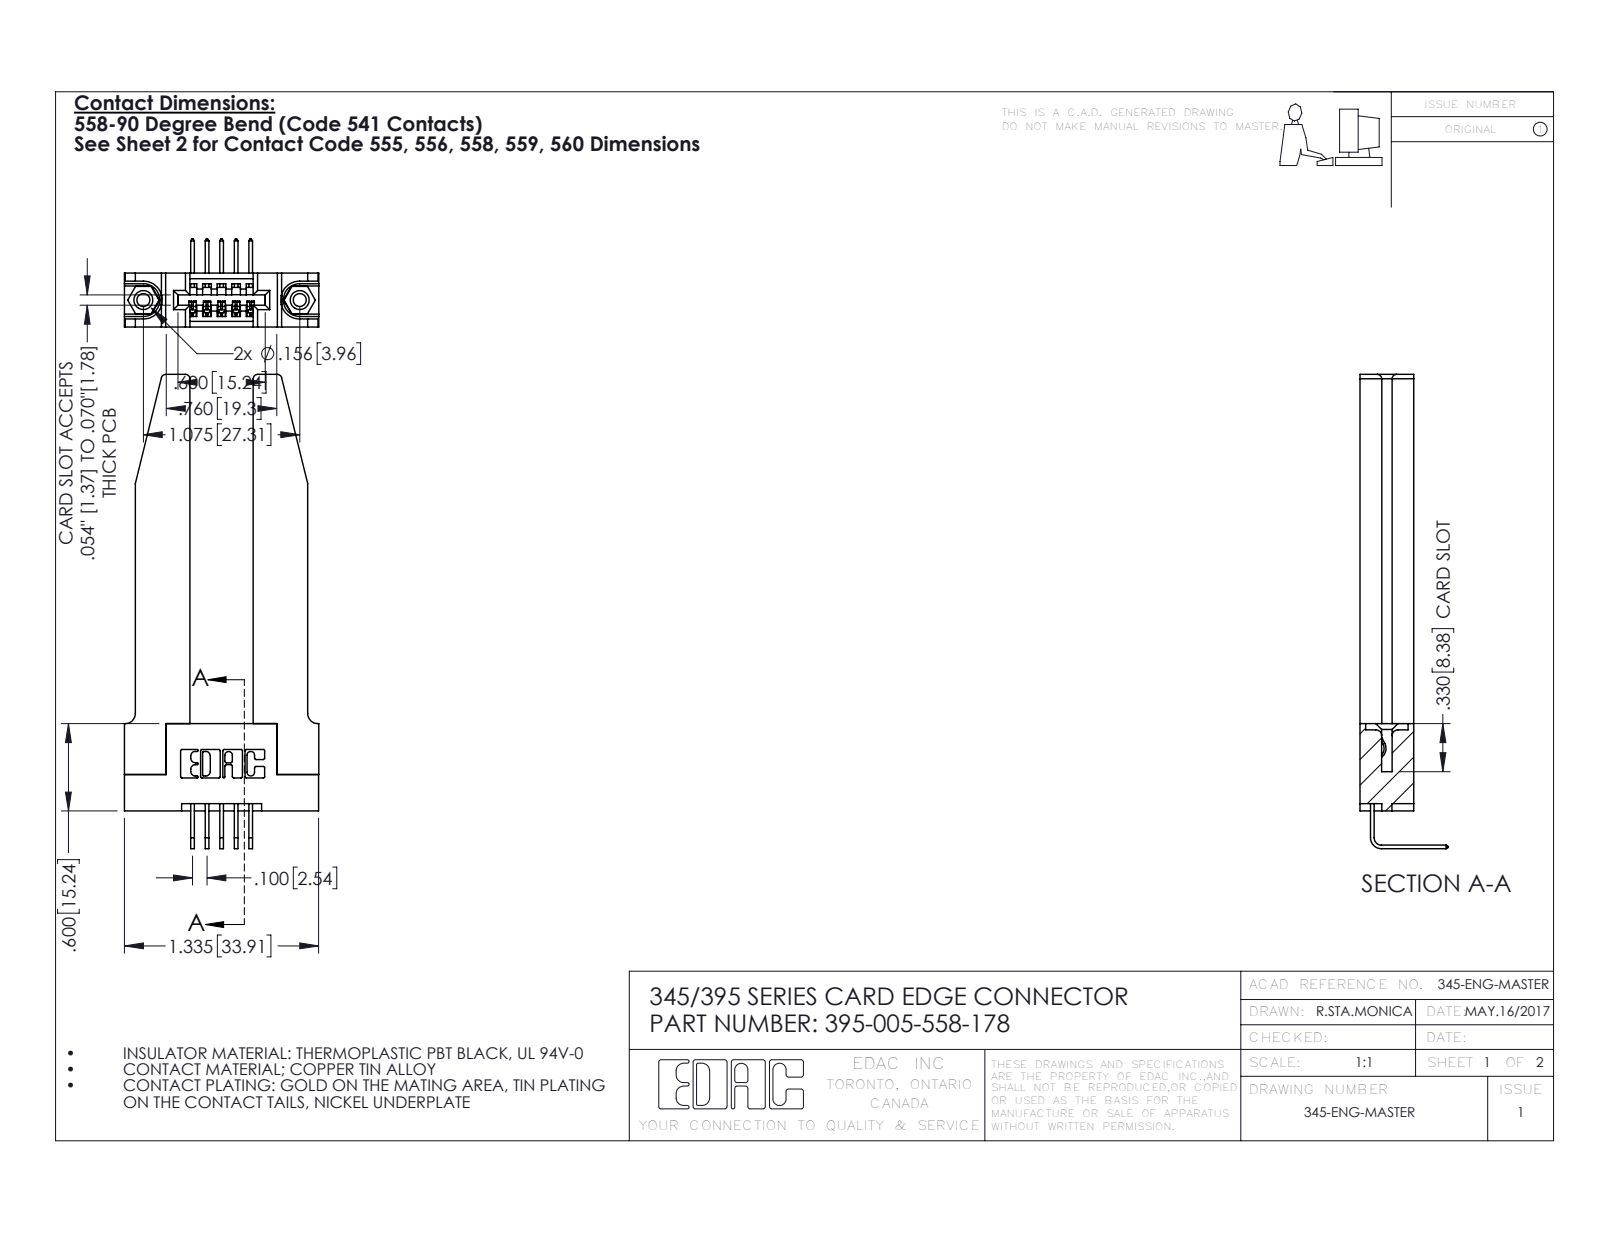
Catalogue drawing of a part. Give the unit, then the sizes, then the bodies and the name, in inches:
Units: inches
Overall size (bounding box): 3.259 × 1.336 × 0.605
Round holes (diameter × count): ⌀0.089 ×2, ⌀0.125 ×2, ⌀0.156 ×2, ⌀0.064 ×1
Round bosses / shafts (diameter × count): ⌀0.155 ×2
Partial cylindrical surfaces — rounded edges, fillets, slot ends (radius × count): R0.01 ×22, R0.006 ×10, R0.03 ×8, R0.007 ×6, R0.031 ×6, R0.026 ×3, R0.031 ×2, R0.04 ×2
Main face-to-face distances: 0.37, 0.15, 0.22, 0.435, 0.072, 0.148, 0.2, 0.077, 0.298, 0.095
Hole centre spacings: 0.27, 0.847, 1.075
Volume: 0.653 in³ · Surface area: 16.03 in²
Bodies: 10 solids, 660 faces (432 planar, 176 cylindrical, 52 other)
Part name (STEP PRODUCT): 395-005-558-178; 345-220-078_345-220-078; 345 Part_Flush Mounting Lugs - 0.156 Dia-TH; 345-292-001_558 Tail - 2 (+1 more)
STEP written by: SolidWorks 2016 (CONFIG_CONTROL_DESIGN)
